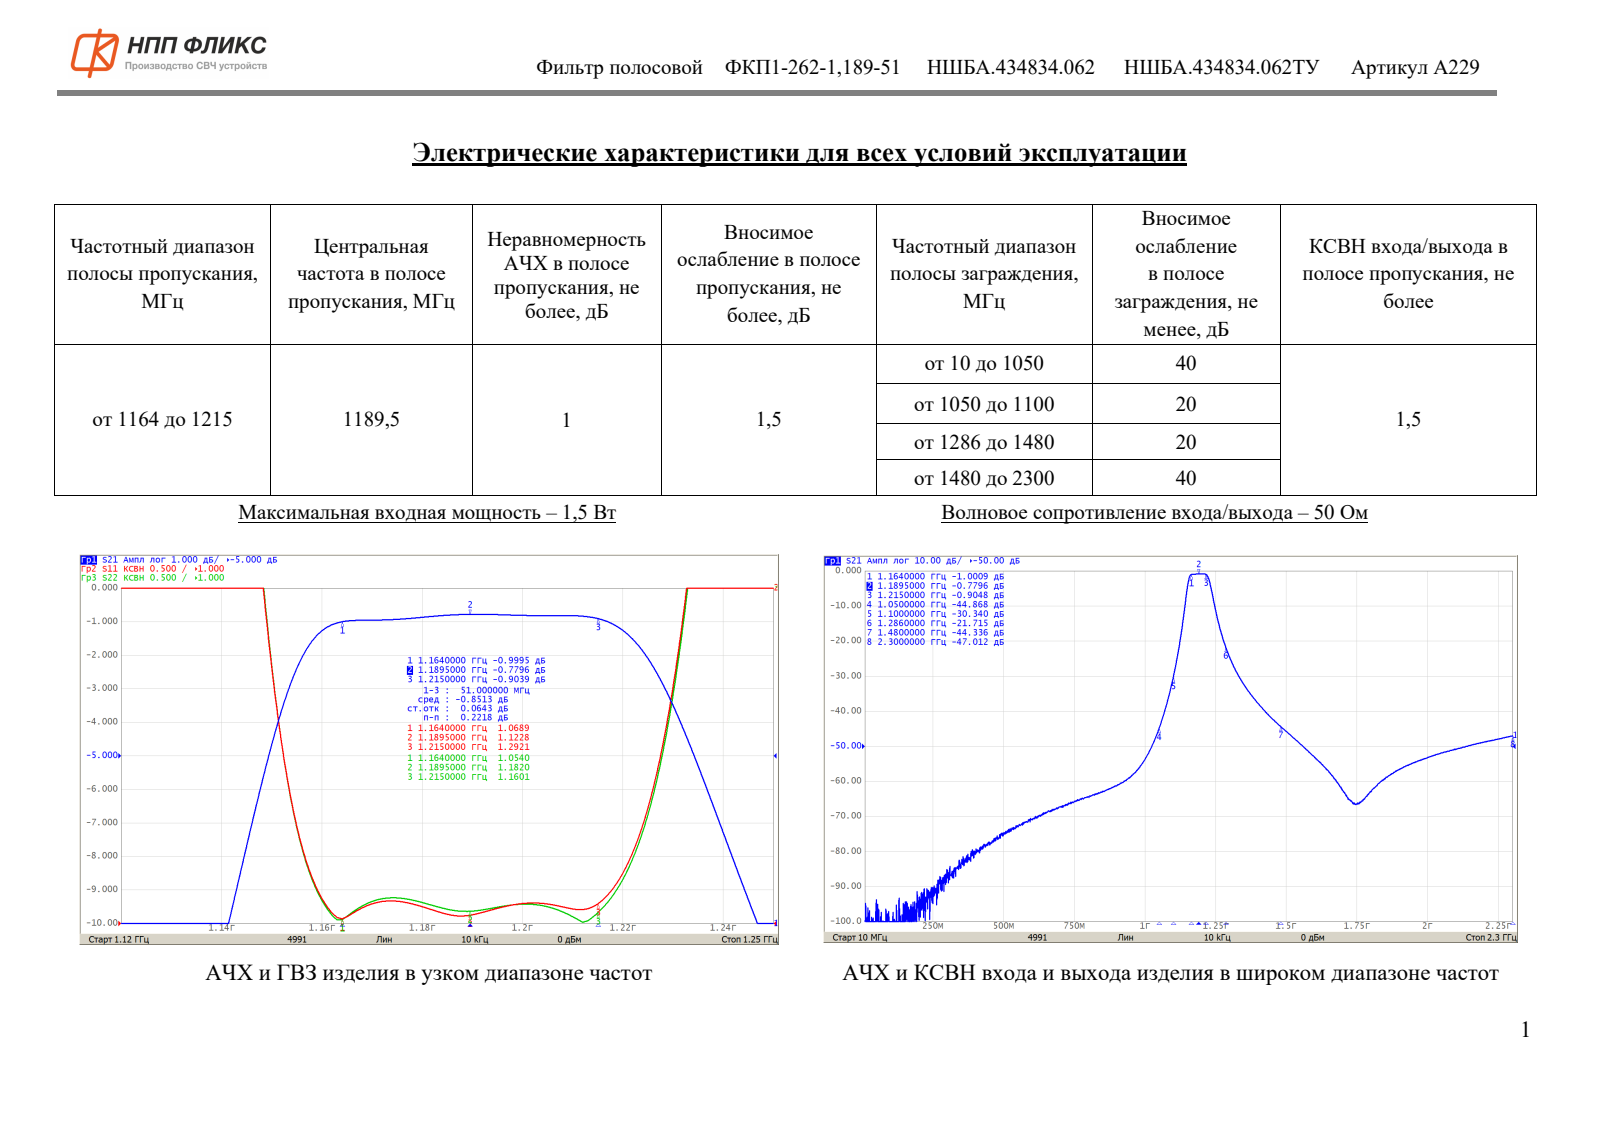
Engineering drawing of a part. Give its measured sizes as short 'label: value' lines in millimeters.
name: НШБА.434834.062_Фильтр ФКП1-262-1,189-51
written by: ASCON Math Kernel (CONFIG_CONTROL_DESIGN)
unit: mm
bodies: 1 solid, 252 faces (195 planar, 19 cylindrical, 38 other)
size: 12.7 × 10.3 × 4.4
volume: 448 mm³; area: 548 mm²
holes: 2× ⌀1
rounds: 3× R0.22, 2× R0.2, 2× R0.4, 2× R1, 1× R0.11, 1× R0.33, 1× R0.39
face distances: 4, 4.2, 8.3, 4.4, 2, 10.3, 1.8, 10.1, 12.7, 1.25
hole spacings: 4.2
